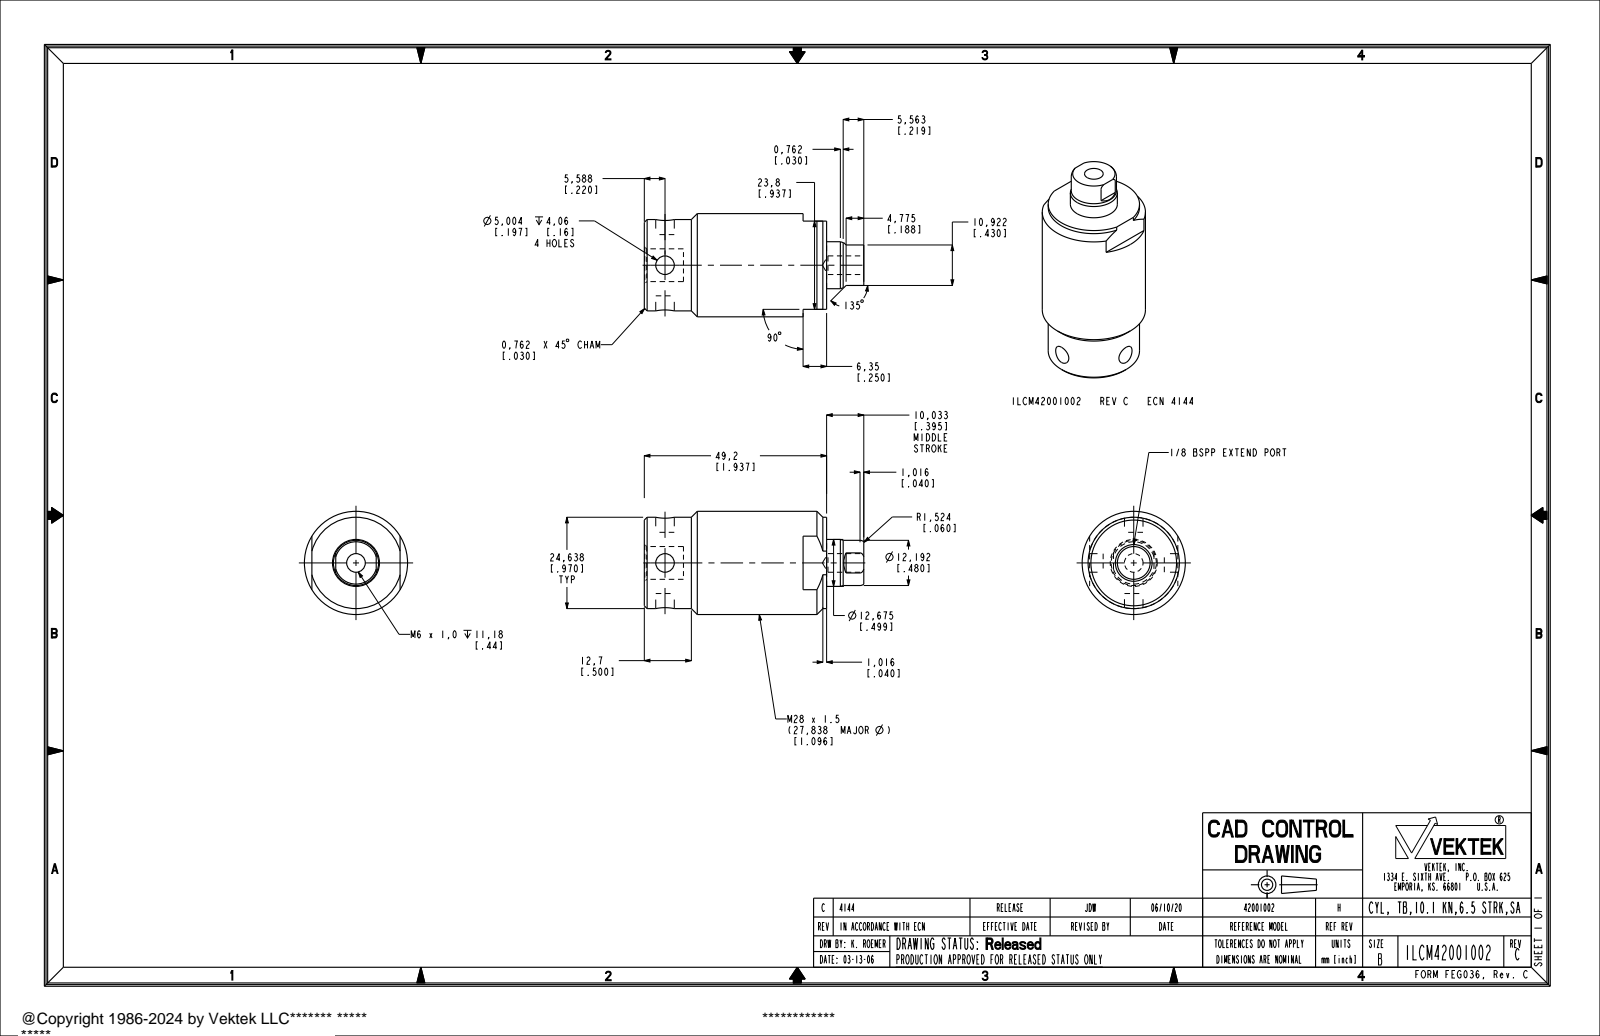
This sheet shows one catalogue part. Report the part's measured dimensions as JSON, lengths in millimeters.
{"part_name": "ILCM42001002", "step_written_by": "PRO/ENGINEER BY PARAMETRIC TECHNOLOGY CORPORATION, 2013320 (AUTOMOTIVE_DESIGN)", "units": "millimeters", "bodies": {"solids": 1, "faces": 54, "planar": 16, "cylindrical": 24, "other": 14}, "overall_size": [59.23, 27.84, 27.84], "volume_mm3": 27729, "surface_area_mm2": 6248, "round_holes": [[5, 2], [5.03, 1], [8.84, 1], [9.91, 1]], "round_bosses_or_shafts": [[27.84, 1], [24.64, 1], [12.68, 1], [12.19, 1]], "face_to_face_distances": [49.2, 59.23, 10.03, 23.8, 10.57, 38.63, 48.66, 6.44, 17.36, 42.85]}
